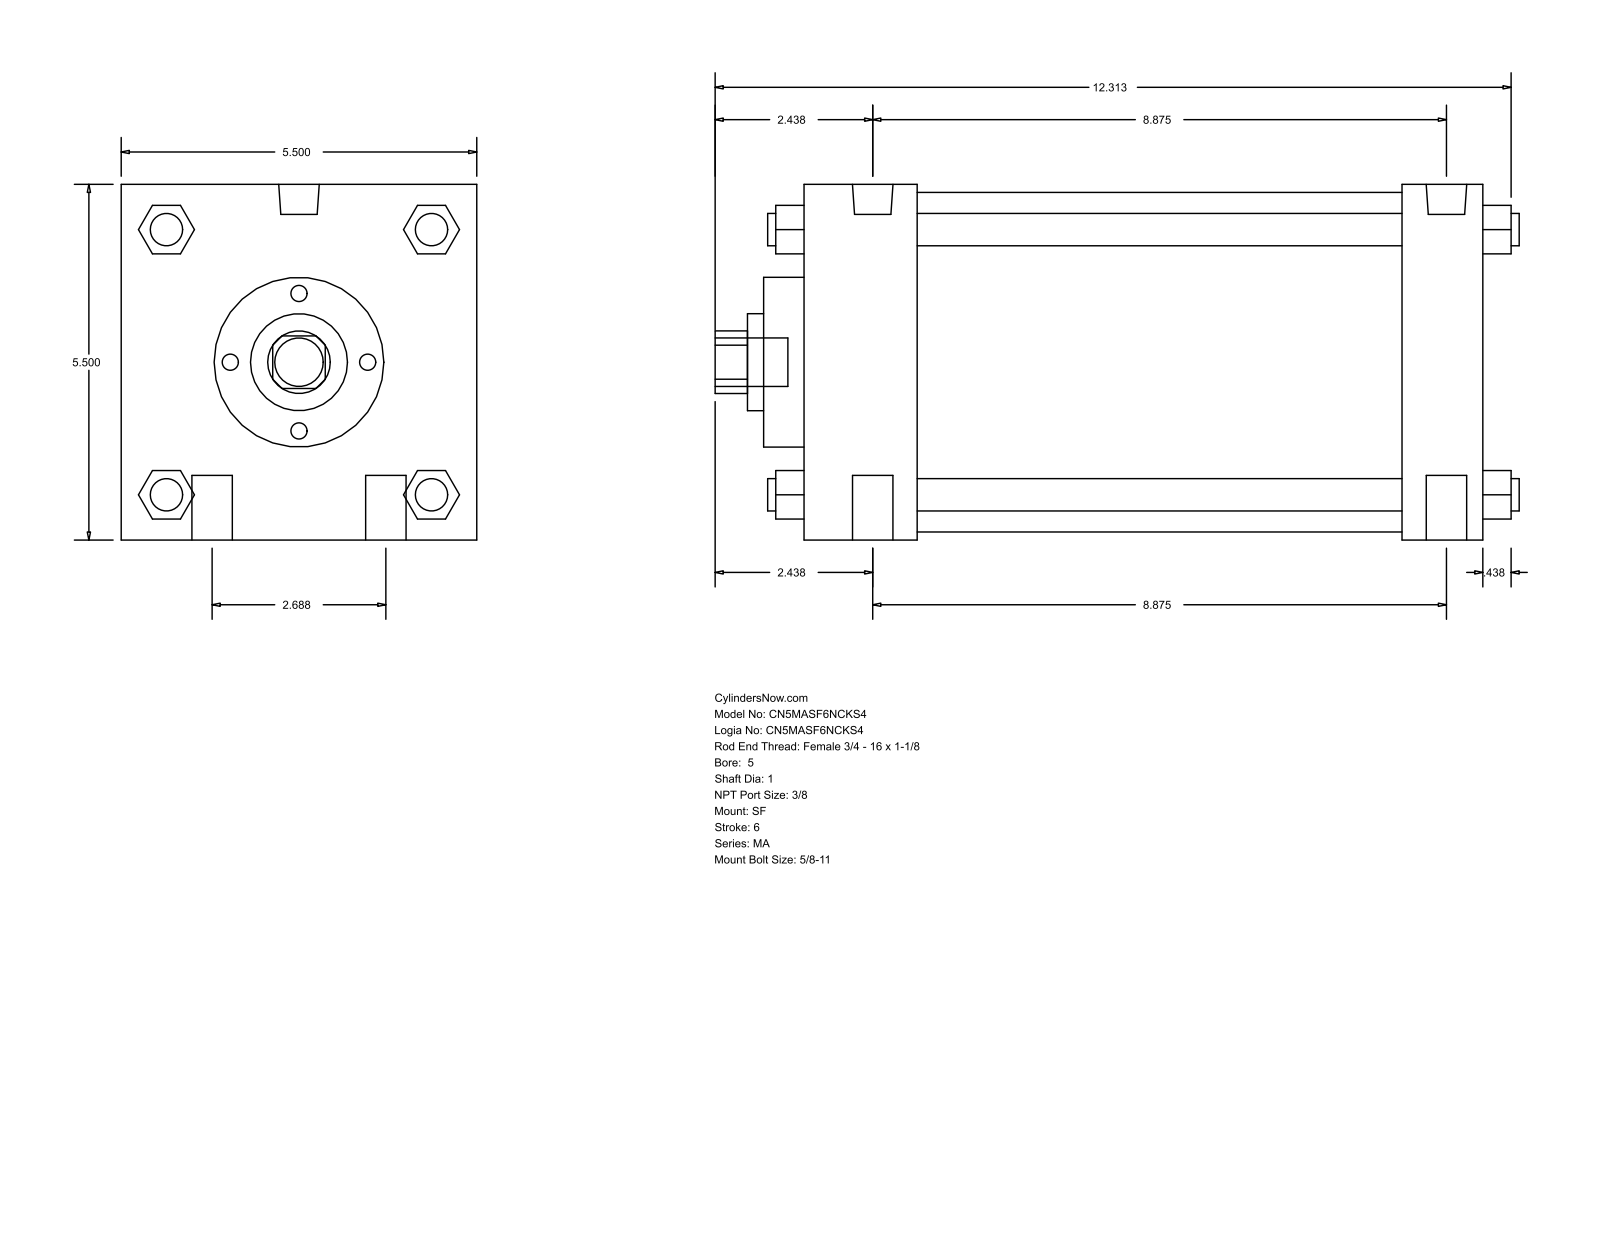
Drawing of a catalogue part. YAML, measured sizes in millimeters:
part_name: "MA_SF__0500_1"
step_written_by: "GSSL Pune (CONFIG_CONTROL_DESIGN)"
units: millimeters
bodies: {solids: 0, faces: 126, planar: 95, cylindrical: 31, other: 0}
overall_size: [315.91, 139.7, 139.7]
round_holes:
  - {diameter: 25.4, count: 1}
  - {diameter: 38.1, count: 1}
  - {diameter: 66.67, count: 1}
  - {diameter: 133.35, count: 1}
round_bosses_or_shafts:
  - {diameter: 15.88, count: 4}
  - {diameter: 12.7, count: 4}
  - {diameter: 15.93, count: 2}
  - {diameter: 11.11, count: 2}
  - {diameter: 19.05, count: 1}
partial_cylinders:
  - {radius: 12.29, count: 1}
face_to_face_distances: [139.7, 266.7, 44.46, 234.96, 190.5, 222.24, 31.74, 15.87, 60.33, 250.83]
